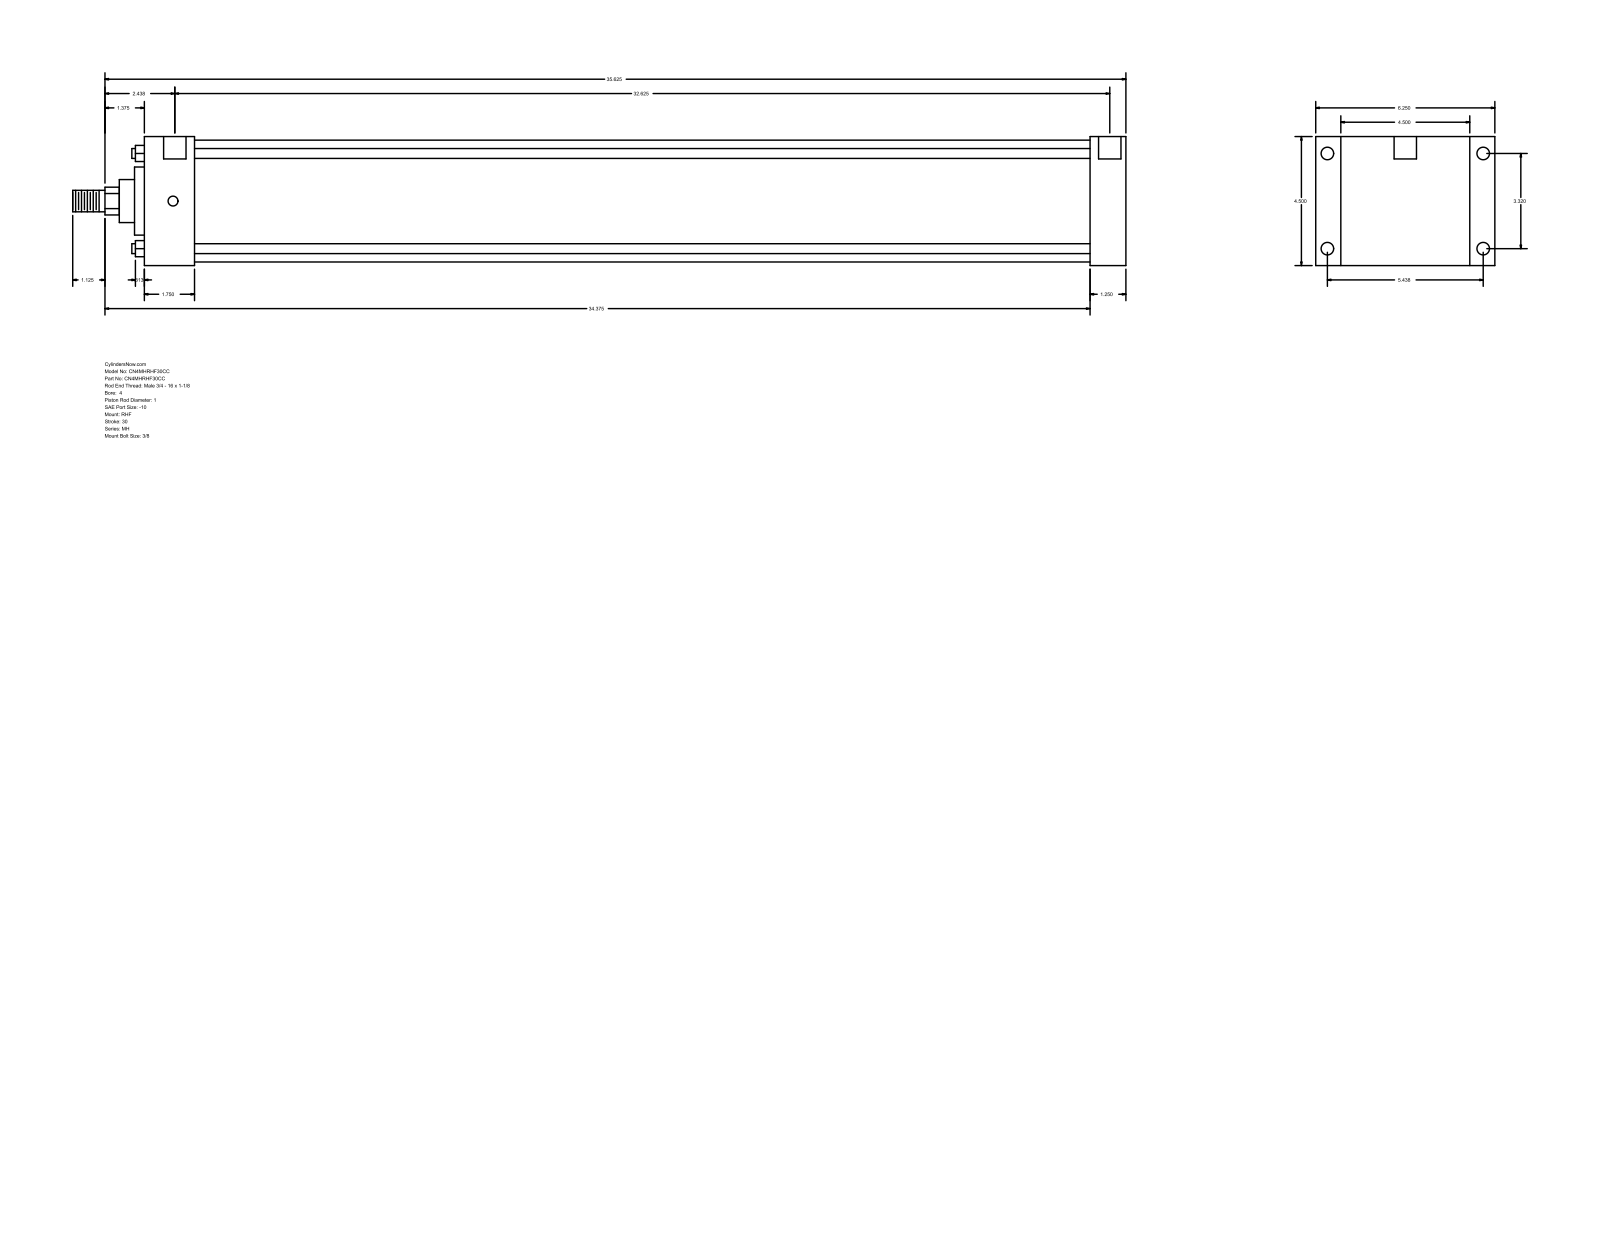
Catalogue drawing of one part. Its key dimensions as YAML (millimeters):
part_name: "MH_RHF__0400_1"
step_written_by: "GSSL Pune (CONFIG_CONTROL_DESIGN)"
units: millimeters
bodies: {solids: 0, faces: 90, planar: 61, cylindrical: 29, other: 0}
overall_size: [933.45, 158.75, 114.3]
round_holes:
  - {diameter: 8.73, count: 4}
  - {diameter: 11.13, count: 4}
  - {diameter: 19.84, count: 2}
round_bosses_or_shafts:
  - {diameter: 8.76, count: 4}
  - {diameter: 107.95, count: 1}
  - {diameter: 60.33, count: 1}
  - {diameter: 38.1, count: 1}
  - {diameter: 25.4, count: 1}
  - {diameter: 19.05, count: 1}
partial_cylinders:
  - {radius: 12.29, count: 1}
face_to_face_distances: [114.3, 869.96, 838.2, 31.76, 22.23, 136.53, 44.46, 793.74, 825.5, 158.76]
hole_center_spacings: [1.58, 84.32, 138.12, 161.82, 830.26, 831.84, 828.68]
